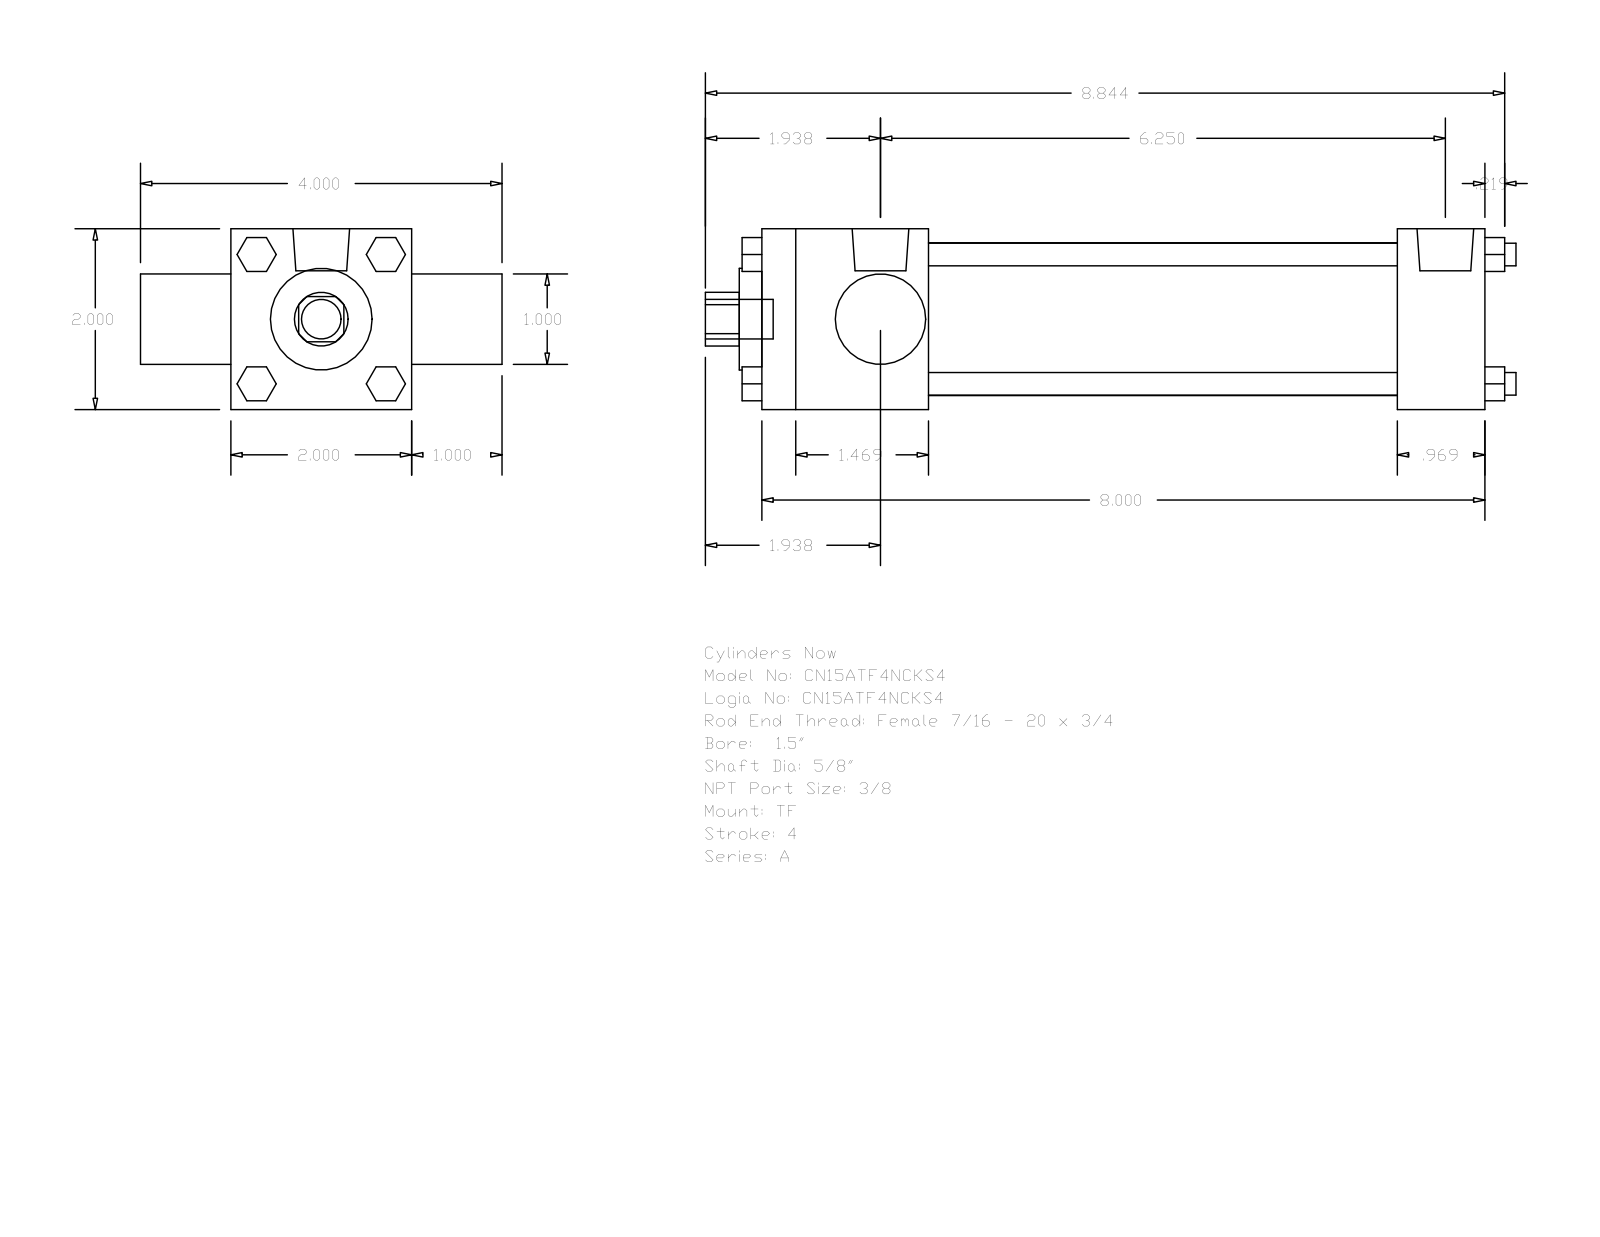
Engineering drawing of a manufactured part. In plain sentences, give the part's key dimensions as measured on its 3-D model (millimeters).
The part is named "A_TF__0150_0.625". Its 3-D file was written by "GSSL Pune (CONFIG_CONTROL_DESIGN)". It is 0 solids with 120 faces: 92 planar, 28 cylindrical and 0 other. Overall it measures 227.81 by 101.6 by 50.8 millimeters. Round holes: 1 of diameter 15.88, 1 of diameter 25.4, 1 of diameter 28.57, 1 of diameter 42.93. Round bosses or shafts: 4 of diameter 6.35, 3 of diameter 5.56, 2 of diameter 15.93, 1 of diameter 11.11. Partial cylindrical surfaces (rounded edges, fillets, slot ends): 1 of radius 7.54. The main face-to-face distances are 50.8, 203.19, 25.4, 76.2, 46.83, 178.59, 131.76, 156.36, 24.6, 9.52.
